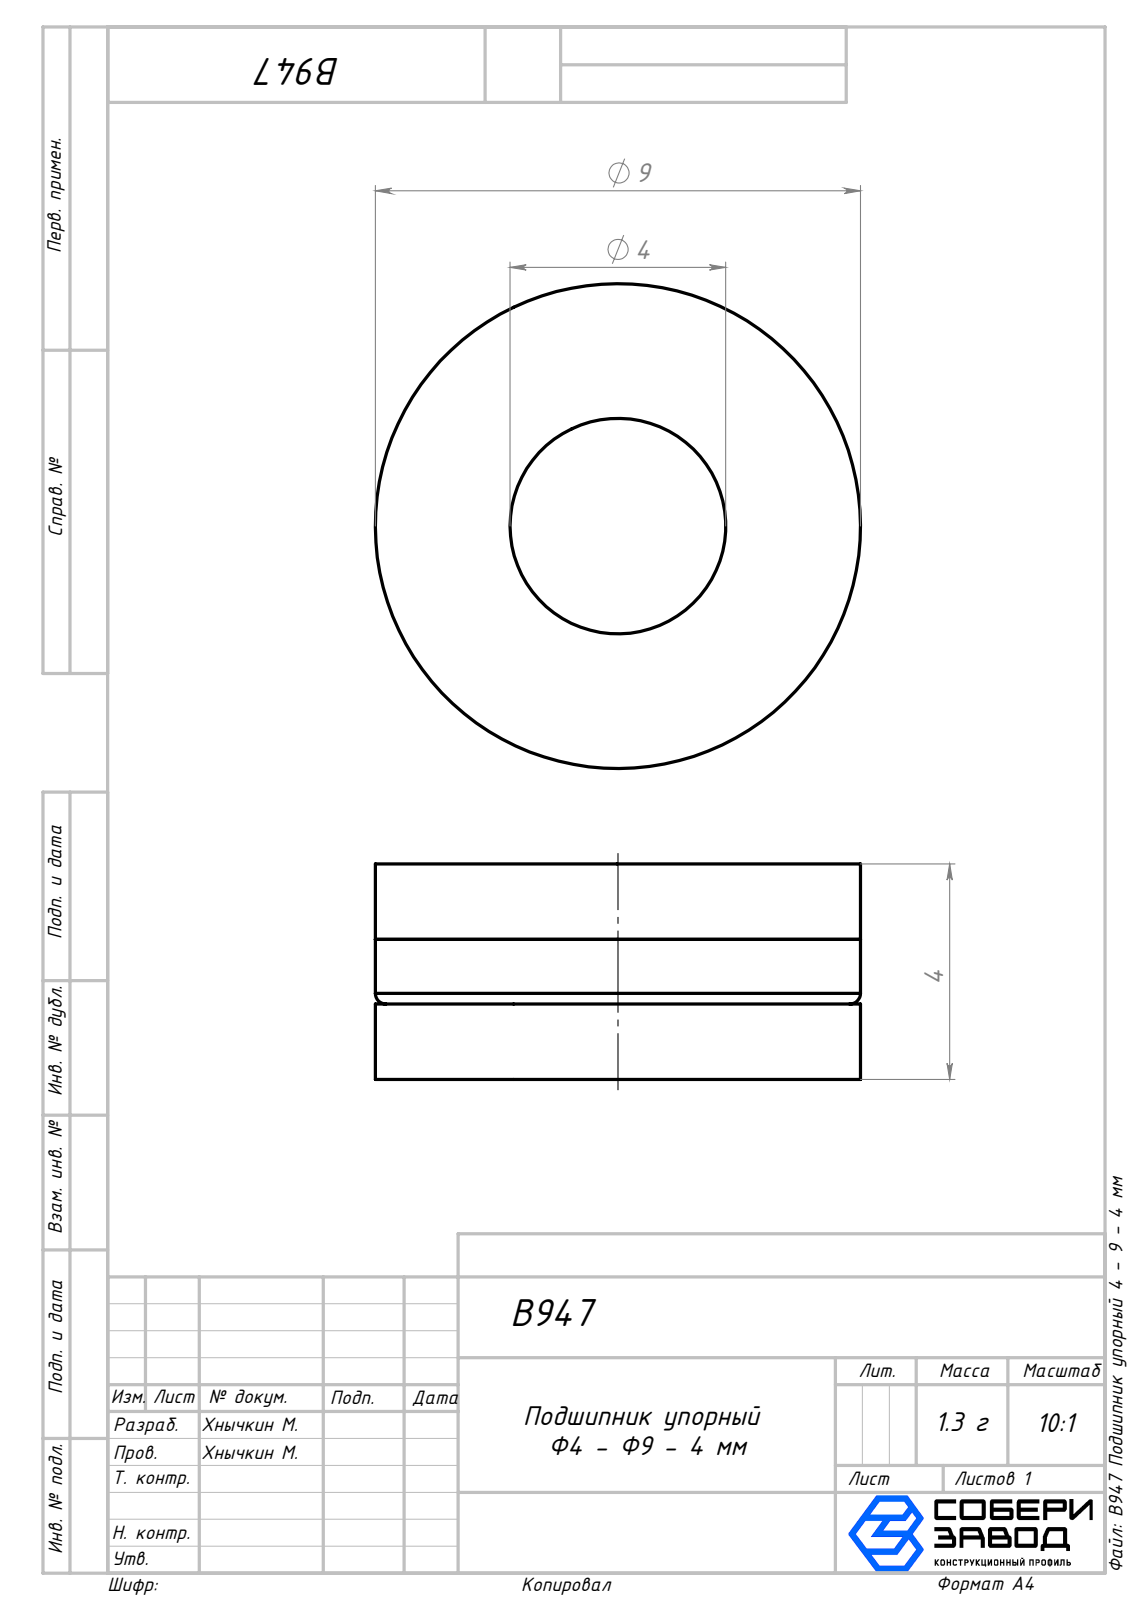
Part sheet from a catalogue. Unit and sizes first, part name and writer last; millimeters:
Units: millimetres
Overall size (bounding box): 9 × 9 × 4
Round holes (diameter × count): ⌀1.6 ×9, ⌀4 ×1, ⌀7.5 ×1, ⌀8.6 ×1
Round bosses / shafts (diameter × count): ⌀9 ×1, ⌀5.5 ×1, ⌀4.4 ×1
Main face-to-face distances: 1.4, 2.6, 4, 1.2, 1.7, 0.9, 2.3, 1.1, 2.9, 1.5
Hole centre spacings: 3.25, 6.4, 2.22, 4.17, 5.63, 4.18, 5.62, 2.23
Volume: 168 mm³ · Surface area: 569 mm²
Bodies: 12 solids, 82 faces (12 planar, 42 cylindrical, 28 other)
Part name (STEP PRODUCT): B947 Первая часть_00; B946 Внутренняя часть_00; B947 Подшипник упорный 4 - 9 - 4 мм; B947 Шарик_00
STEP written by: SolidWorks 2026 (AUTOMOTIVE_DESIGN)
